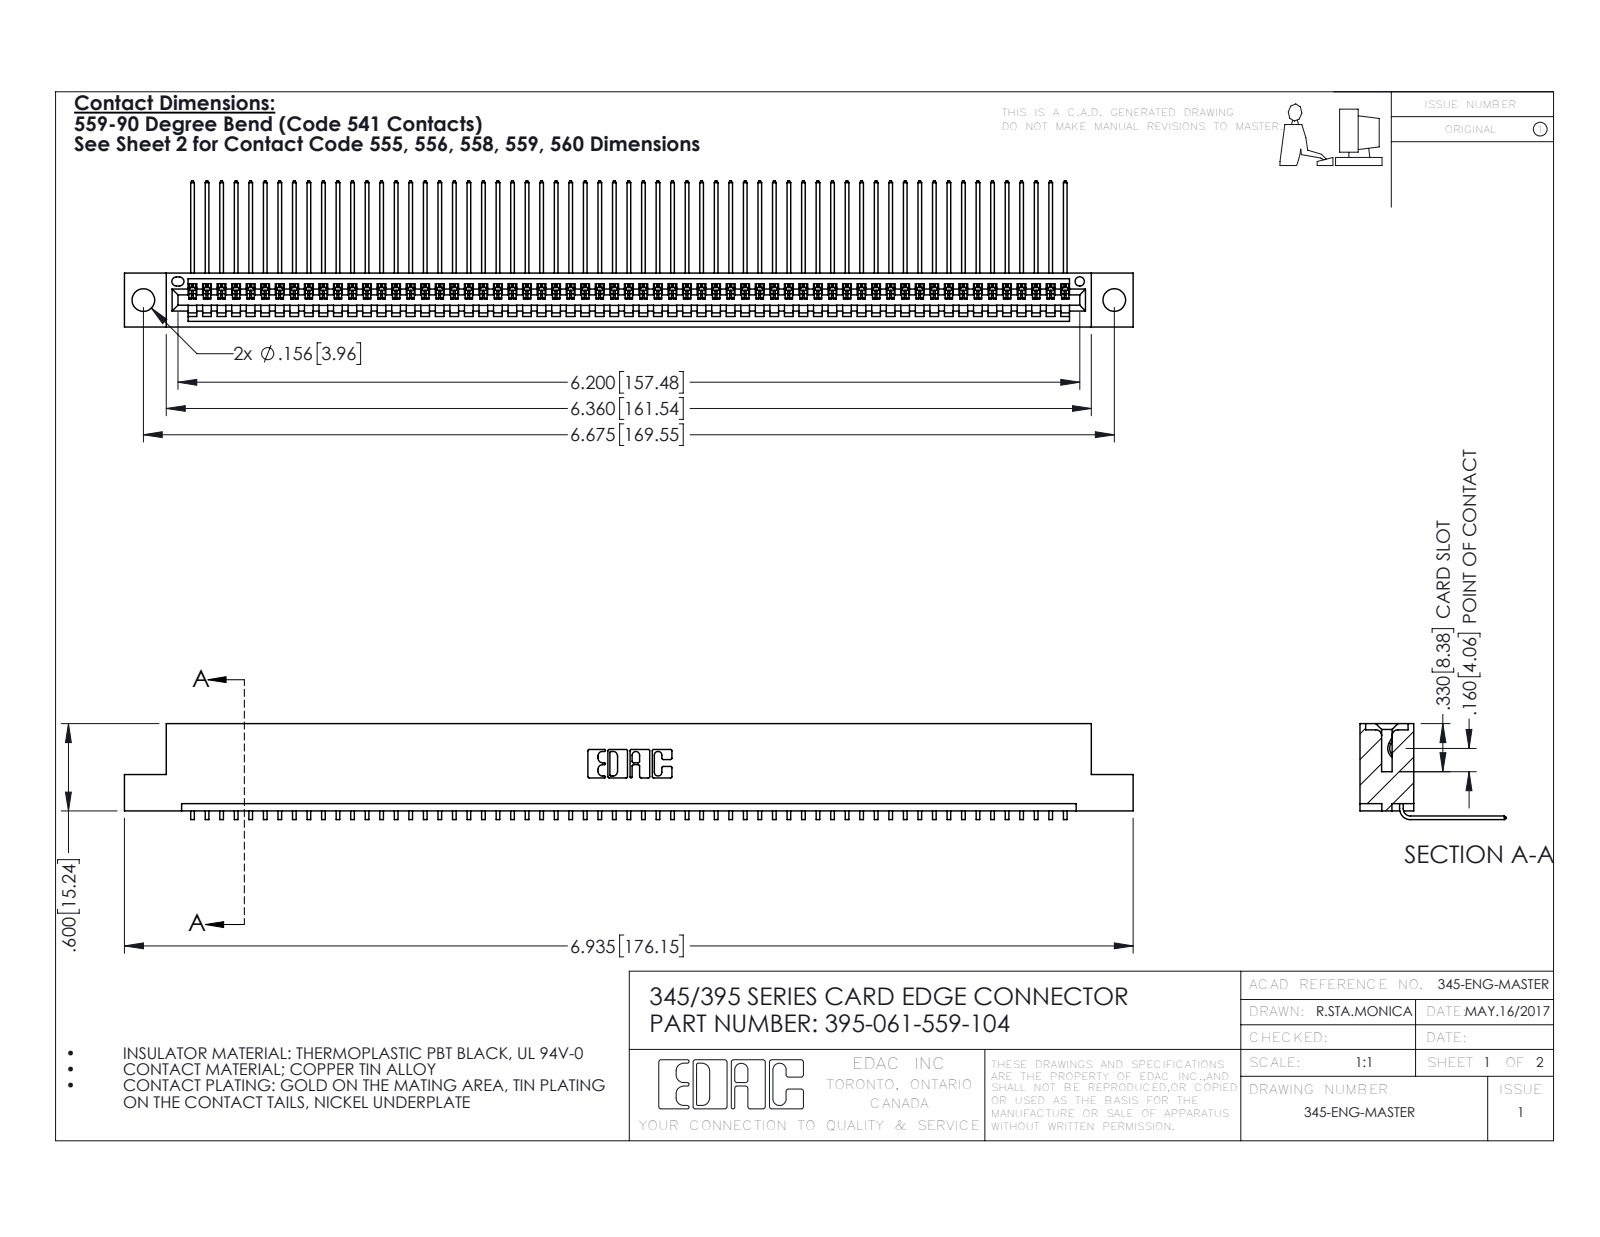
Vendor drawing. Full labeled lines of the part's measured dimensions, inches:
Part name (STEP PRODUCT): 395-061-559-104; 345 Part_Flush Mounting Lugs - 0.156 Dia-TH; 345-292-001_558 559 Tail - 1
STEP written by: SolidWorks 2016 (CONFIG_CONTROL_DESIGN)
Units: inches
Bodies: 62 solids, 3786 faces (2642 planar, 1144 cylindrical, 0 other)
Overall size (bounding box): 6.935 × 1.005 × 0.659
Volume: 1.038 in³ · Surface area: 36.98 in²
Round holes (diameter × count): ⌀0.156 ×2, ⌀0.064 ×1
Partial cylindrical surfaces — rounded edges, fillets, slot ends (radius × count): R0.006 ×122, R0.01 ×22, R0.007 ×6, R0.031 ×6, R0.026 ×3, R0.031 ×2, R0.04 ×2, R0.014 ×1
Main face-to-face distances: 0.298, 0.072, 0.37, 0.2, 0.098, 0.272, 0.025, 0.225, 0.149, 0.072
Hole centre spacings: 0.27, 6.439, 6.675
